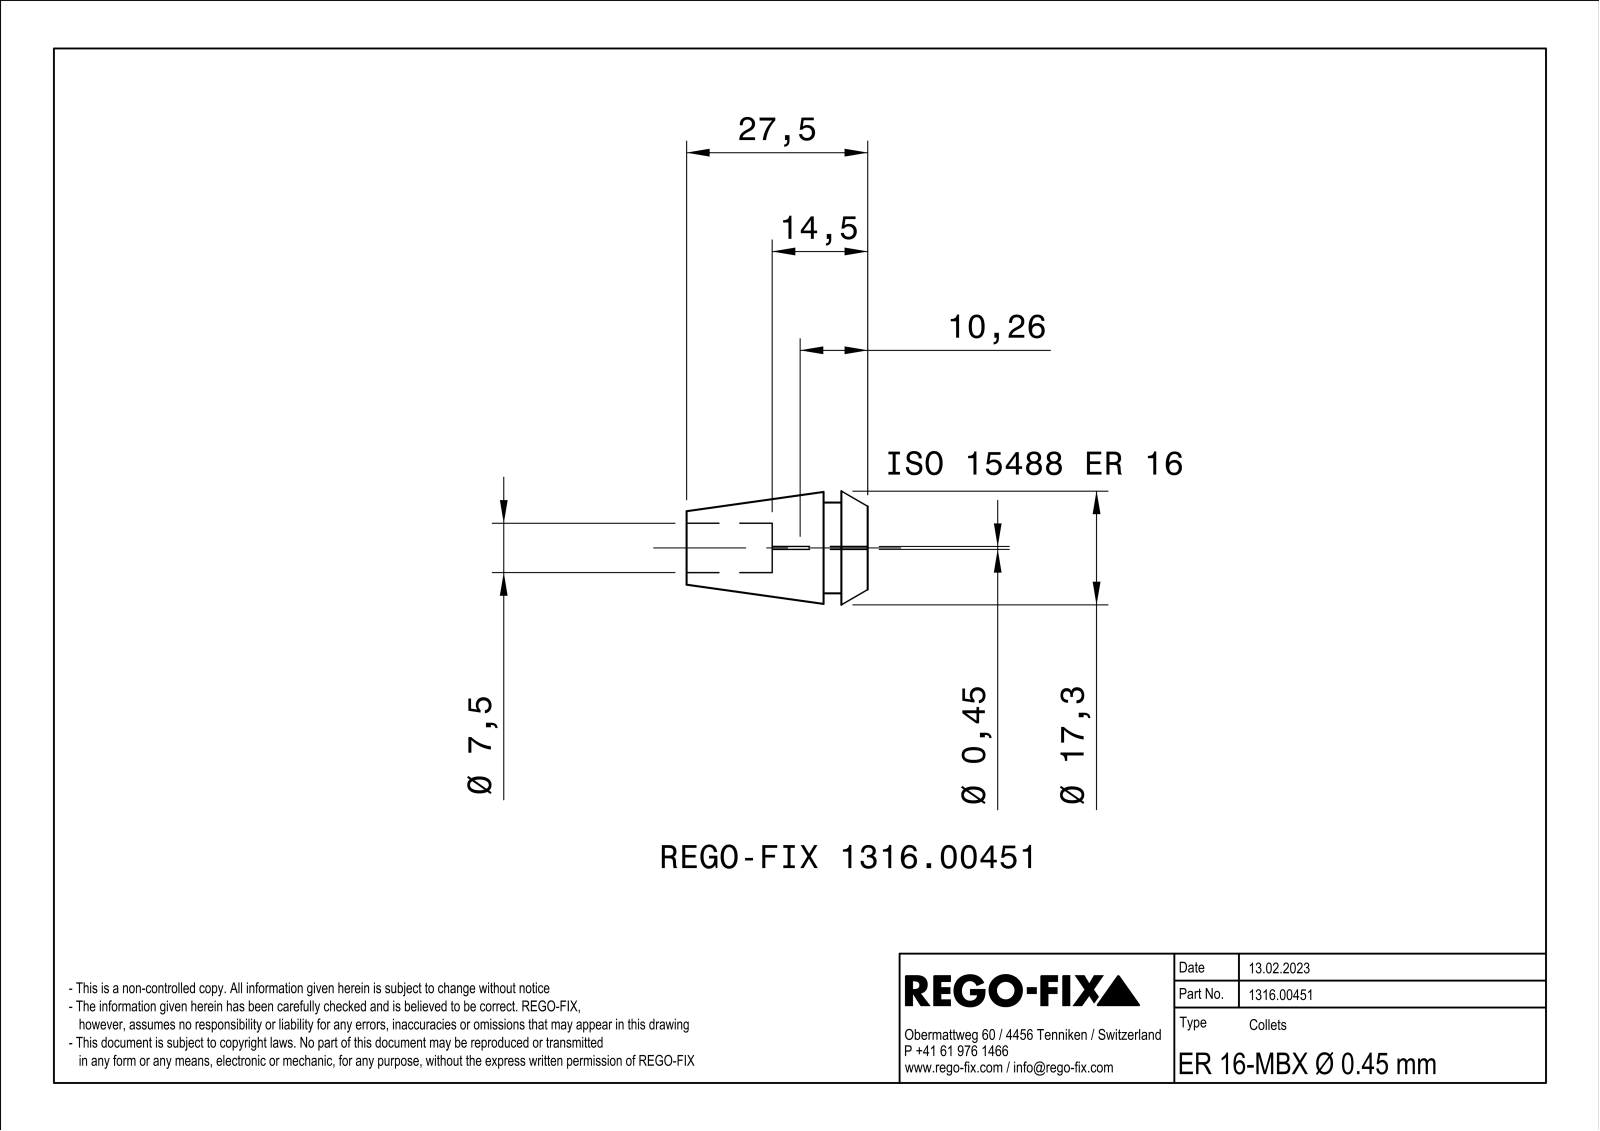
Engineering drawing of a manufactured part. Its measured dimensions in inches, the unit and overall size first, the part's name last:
Units: inches
Overall size (bounding box): 1.083 × 0.666 × 0.665
Round holes (diameter × count): ⌀0.079 ×3, ⌀0.295 ×1
Round bosses / shafts (diameter × count): ⌀0.543 ×1
Partial cylindrical surfaces — rounded edges, fillets, slot ends (radius × count): R0.004 ×3, R0.984 ×3, R0.009 ×1
Main face-to-face distances: 0.02, 0.031, 0.264, 0.157, 0.106, 1.083, 0.925, 0.819, 0.571, 0.413
Hole centre spacings: 0.083, 0.143
Volume: 0.203 in³ · Surface area: 5.157 in²
Bodies: 1 solid, 109 faces (36 planar, 27 cylindrical, 46 other)
Part name (STEP PRODUCT): NOCUT
STEP written by: SIEMENS PLM Software Solid Edge ST10 (AUTOMOTIVE_DESIGN)
